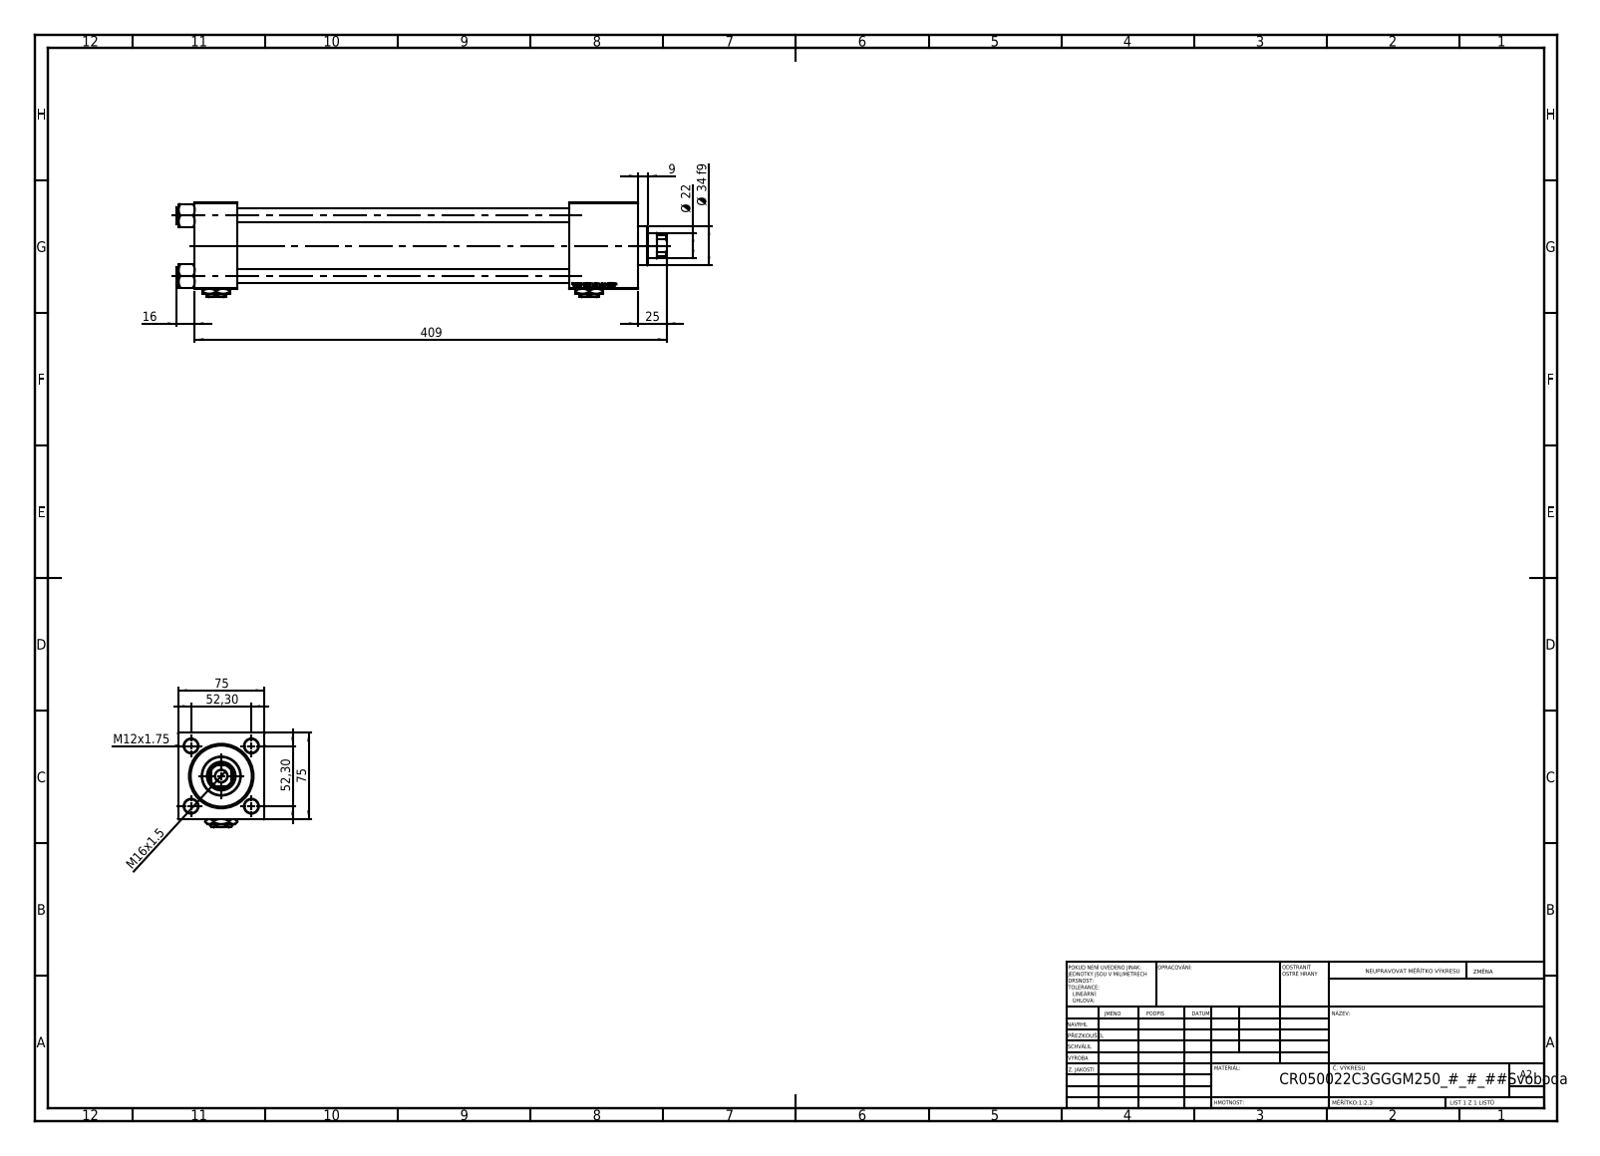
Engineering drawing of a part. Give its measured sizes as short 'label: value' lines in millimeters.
name: V215CR_VCP_C; V215CR_C_TYCINKA; Zatka_pro_OIL_PORT; V215CR_C_Body (+2 more)
written by: SolidWorks 2019 (CONFIG_CONTROL_DESIGN)
unit: mm
bodies: 13 solids, 1249 faces (573 planar, 98 cylindrical, 578 other)
size: 425 × 82 × 75.54
volume: 957 620 mm³; area: 279 050 mm²
holes: 4× ⌀12, 2× ⌀7, 2× ⌀20.96, 2× ⌀30, 1× ⌀10.5, 1× ⌀22, 1× ⌀25, 1× ⌀41, 1× ⌀50, 1× ⌀53
bosses: 4× ⌀15, 1× ⌀56, 1× ⌀34
rounds: 1× R10.5
face distances: 75, 37, 384, 347, 325, 59, 288, 355.3, 318.3, 30.3
hole spacings: 36.98, 52.3, 73.96, 323.5
